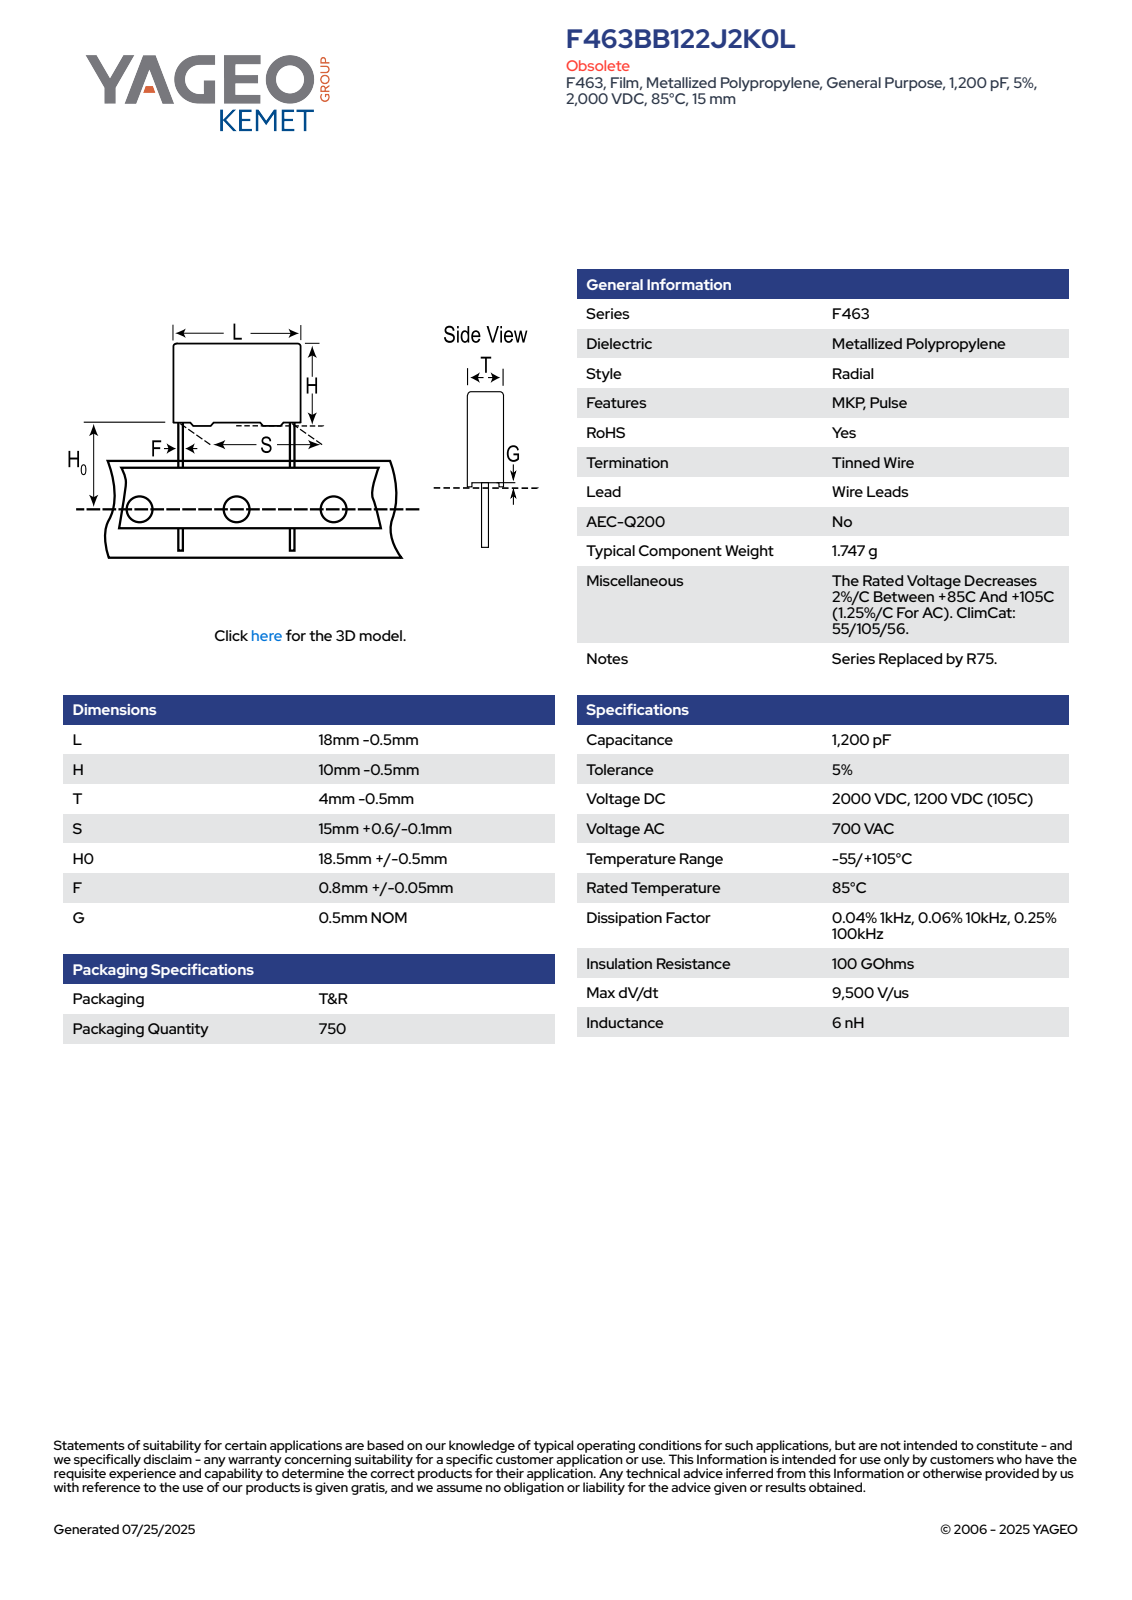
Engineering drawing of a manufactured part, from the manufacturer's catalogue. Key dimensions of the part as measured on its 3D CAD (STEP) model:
Part name (STEP PRODUCT): CFR_RBG_18X10X4_L17.5H9.5T3.5S15H019F0.85G0.5
STEP written by: SolidWorks 2014 (AUTOMOTIVE_DESIGN)
Units: millimetres
Bodies: 4 solids, 89 faces (81 planar, 8 cylindrical, 0 other)
Overall size (bounding box): 28.5 × 17.5 × 3.5
Volume: 572 mm³ · Surface area: 641 mm²
Round bosses / shafts (diameter × count): ⌀0.85 ×2
Partial cylindrical surfaces — rounded edges, fillets, slot ends (radius × count): R0.5 ×4
Main face-to-face distances: 3.5, 9, 17.5, 3.3, 3.1, 0.5, 9.5, 19, 19.5, 28.5
